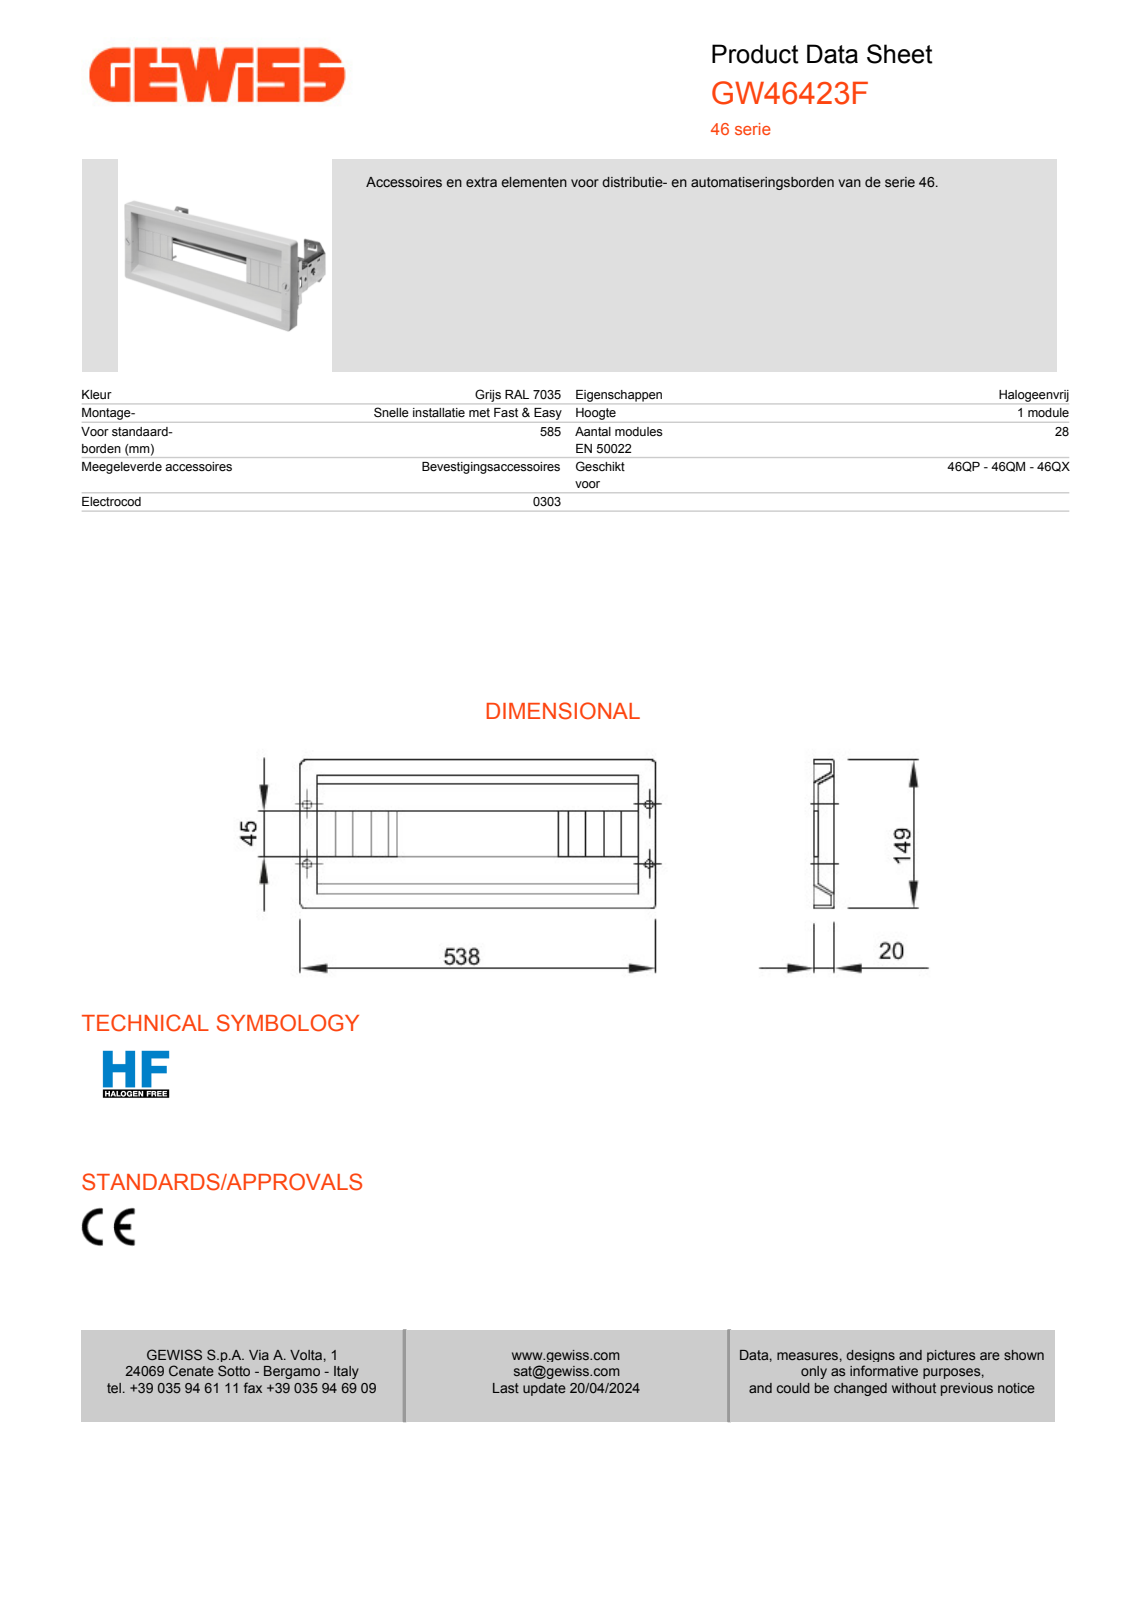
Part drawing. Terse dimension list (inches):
name: 55710628_C2XX_MOSTRINA_CON_FINE; 55721450XXXX_GUIDA_DIN_28_M_H15; GW46423F_ASM
written by: CREO PARAMETRIC BY PTC INC, 2020354 (CONFIG_CONTROL_DESIGN)
unit: in
bodies: 2 solids, 1076 faces (783 planar, 247 cylindrical, 46 other)
size: 21.378 × 5.866 × 4.719
volume: 24.54 in³; area: 537.9 in²
holes: 4× ⌀0.177, 4× ⌀0.256, 2× ⌀0.128, 2× ⌀0.165, 2× ⌀0.181, 2× ⌀0.217, 1× ⌀0.236, 1× ⌀0.315
bosses: 2× ⌀0.567, 2× ⌀0.528, 2× ⌀0.378
rounds: 44× R0.059, 38× R0.039, 14× R0.02, 8× R0.049, 6× R0.079, 4× R0.01, 4× R0.045, 4× R0.157
face distances: 0.118, 0.059, 0.669, 5.748, 0.787, 0.551, 2.52, 3.189, 2.402, 2.461
hole spacings: 0.571, 19.823, 1.19, 19.252, 20.394, 20.006, 20.006, 20.575
